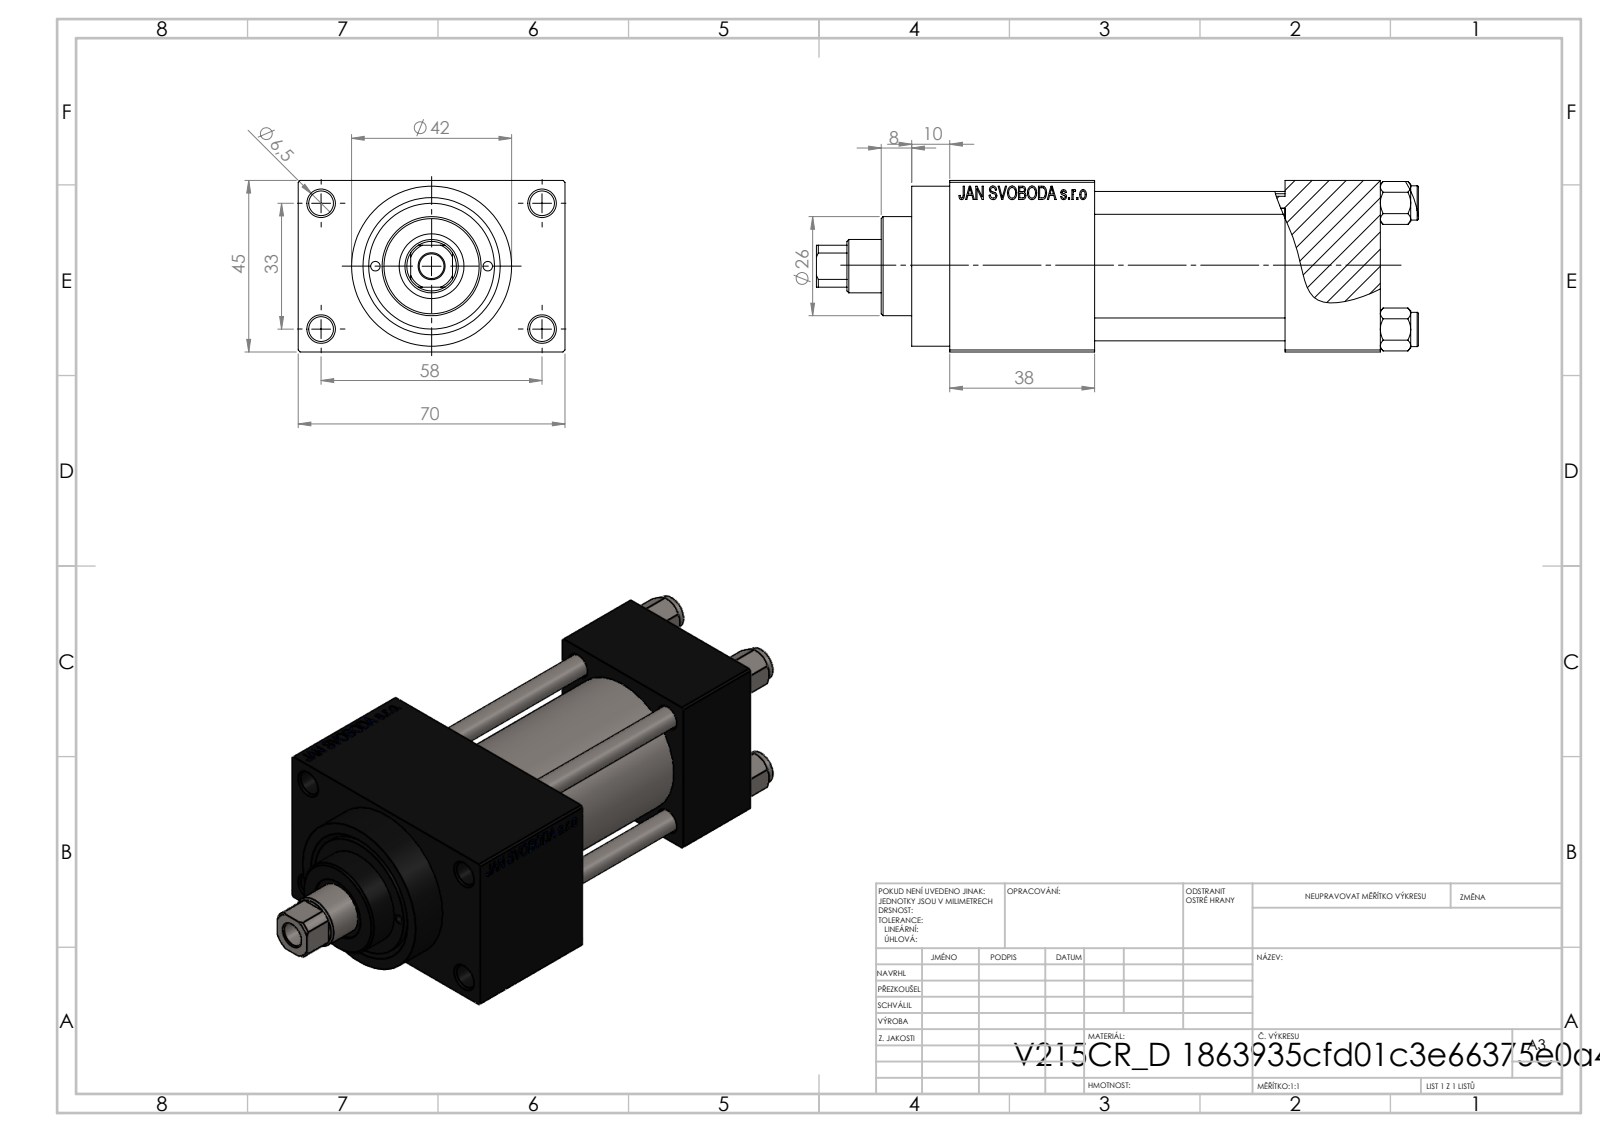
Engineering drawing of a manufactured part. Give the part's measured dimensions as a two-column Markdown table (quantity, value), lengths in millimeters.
| quantity | value |
| --- | --- |
| part name | V215CR_VCP_D; V215CR_D_Body; NUT_M5_D; V215_VC_A (+1 more) |
| STEP written by | SolidWorks 2019 (CONFIG_CONTROL_DESIGN) |
| units | millimeters |
| bodies | 11 solids, 1110 faces (498 planar, 92 cylindrical, 520 other) |
| overall size | 158 × 70 × 45 |
| volume | 230 158 mm³ |
| surface area | 75 379 mm² |
| round holes (diameter × count) | 6.5 × 5, 6 × 4, 2.5 × 2, 7 × 2, 13.16 × 2, 20 × 2, 14 × 1, 17 × 1, 24 × 1, 32 × 1, 33 × 1 |
| round bosses / shafts (diameter × count) | 9 × 4, 42 × 1, 38 × 1, 26 × 1 |
| partial cylindrical surfaces (radius × count) | 6.5 × 1 |
| main face-to-face distances | 45, 25, 50, 12.5, 75, 57.5, 88, 38, 113, 70 |
| hole center spacings | 12.4, 16.7, 21.8, 23.48, 33.2, 33.37, 35.35, 35.47 |
